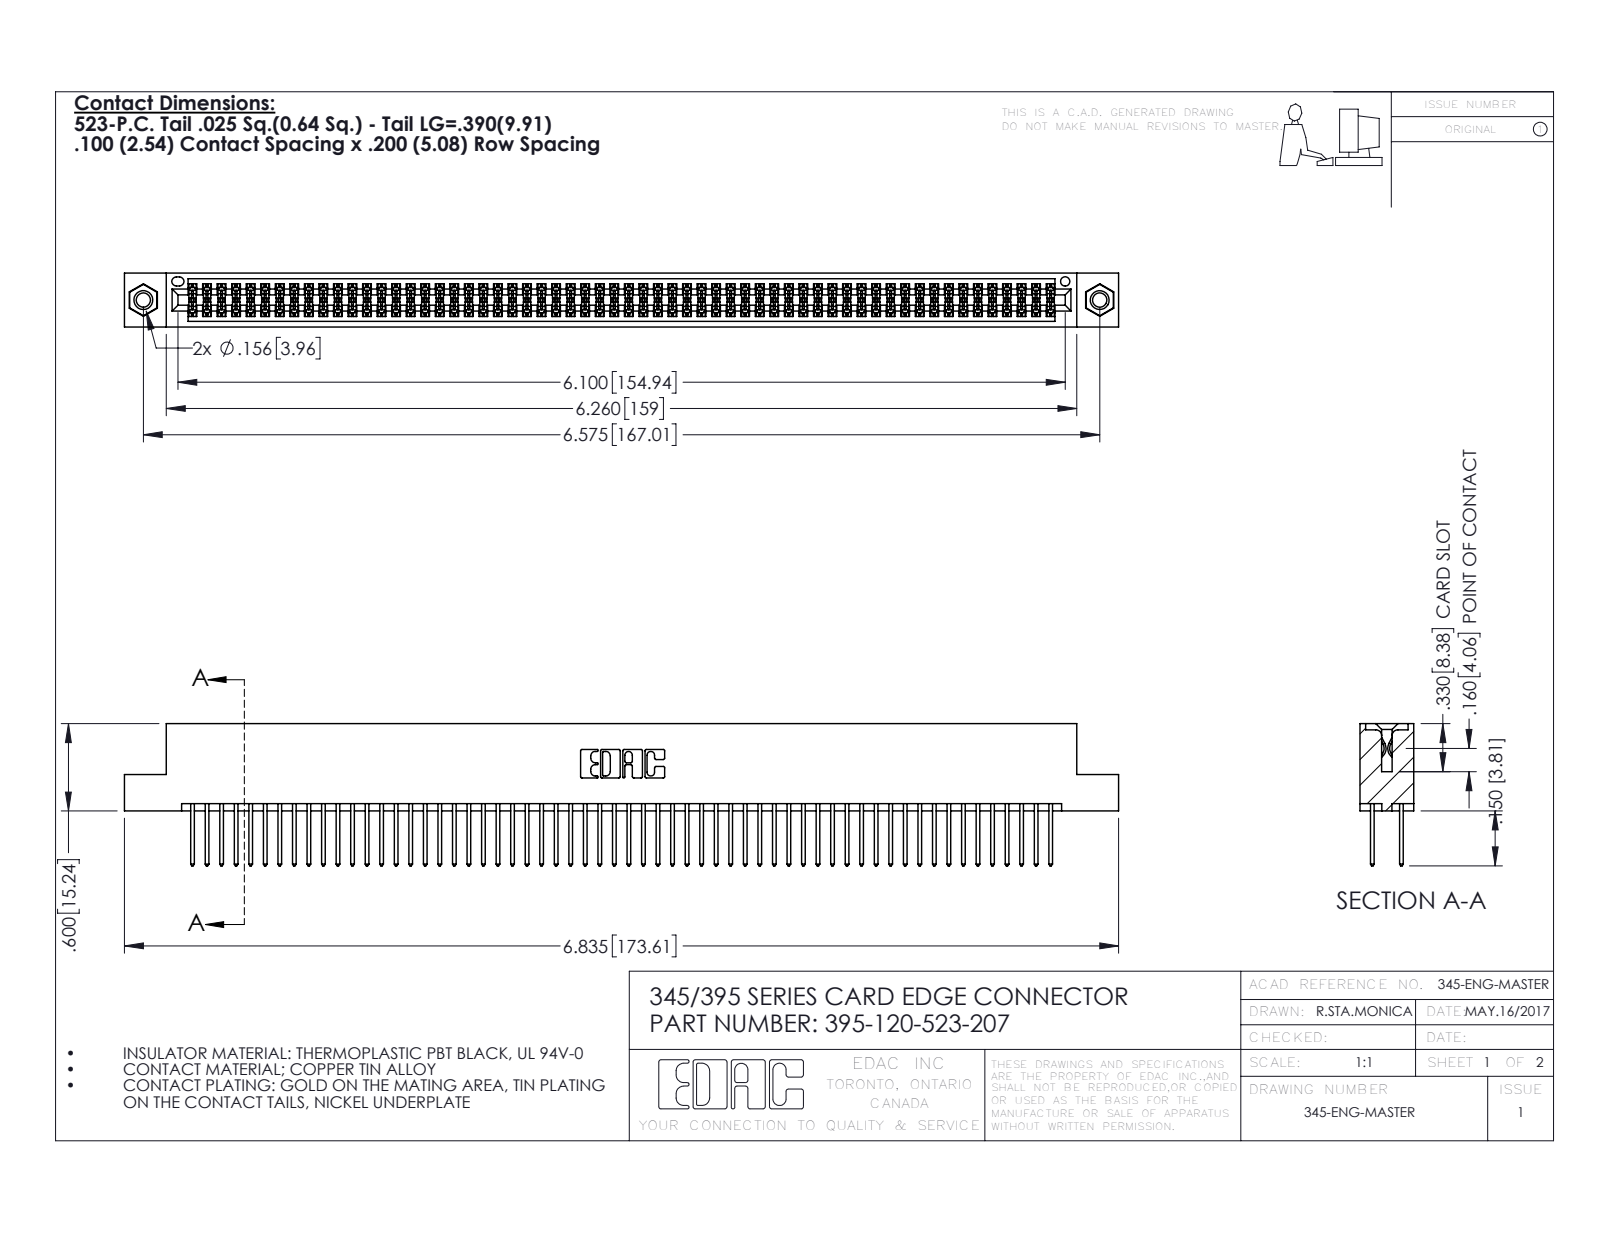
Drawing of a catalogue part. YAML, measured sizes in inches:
part_name: "345-250-001_345-250-005-103; 345 Part_Flush Mounting Lugs - 0.156 Dia-TI; 395-120-523-207; 345-292-001_345-293-123"
step_written_by: "SolidWorks 2016 (CONFIG_CONTROL_DESIGN)"
units: inches
bodies: {solids: 123, faces: 6186, planar: 4072, cylindrical: 2098, other: 16}
overall_size: [6.835, 0.977, 0.37]
volume: 1.054
surface_area: 41.85
round_holes:
  - {diameter: 0.098, count: 2}
  - {diameter: 0.125, count: 2}
  - {diameter: 0.156, count: 2}
  - {diameter: 0.064, count: 1}
round_bosses_or_shafts:
  - {diameter: 0.155, count: 2}
partial_cylinders:
  - {radius: 0.006, count: 180}
  - {radius: 0.01, count: 120}
  - {radius: 0.01, count: 22}
  - {radius: 0.007, count: 6}
  - {radius: 0.031, count: 6}
  - {radius: 0.026, count: 3}
  - {radius: 0.014, count: 2}
  - {radius: 0.019, count: 2}
face_to_face_distances: [0.072, 0.298, 0.2, 0.098, 0.272, 0.025, 0.37, 0.225, 0.175, 0.149]
hole_center_spacings: [0.27, 6.339, 6.575]
